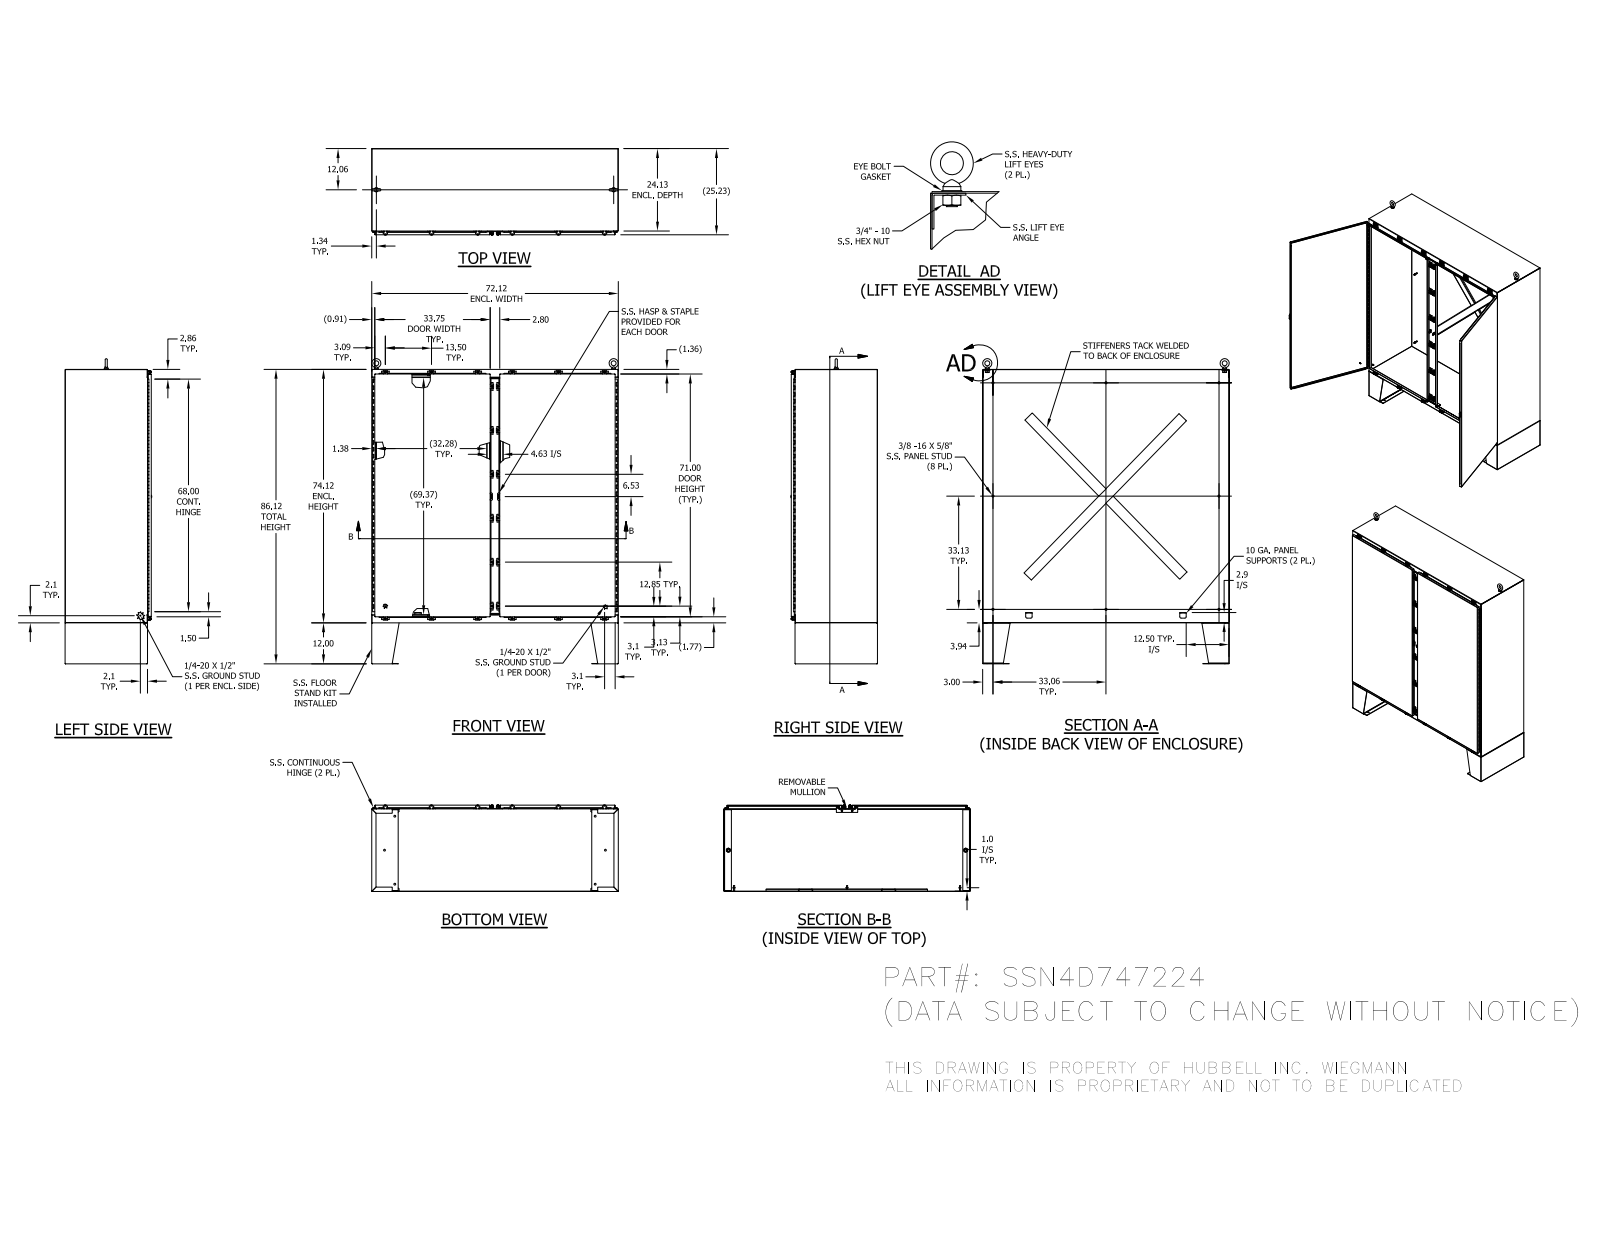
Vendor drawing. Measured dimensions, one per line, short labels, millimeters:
name: 328131P-68_1; SSFK24B_1; 32912_1; 30824_1 (+8 more)
written by: SolidWorks 2014 (AUTOMOTIVE_DESIGN)
unit: mm
bodies: 185 solids, 6996 faces (2802 planar, 2798 cylindrical, 1396 other)
size: 2266.9 × 1832 × 644
volume: 33 920 000 mm³; area: 28 090 000 mm²
holes: 48× ⌀2.8, 24× ⌀5.4, 24× ⌀7.1, 24× ⌀7.6, 18× ⌀14.3, 16× ⌀9.5, 4× ⌀5, 4× ⌀5.1, 4× ⌀7.9, 4× ⌀8, 2× ⌀3.6, 2× ⌀4
bosses: 31× ⌀6.4, 24× ⌀13.2, 24× ⌀12.7, 24× ⌀8.9, 10× ⌀8.4, 8× ⌀15.9, 4× ⌀11.1, 3× ⌀8.6
rounds: 268× R0.8, 62× R3.2, 48× R3.6, 39× R6.4, 34× R1.6, 24× R0.8, 24× R2.5, 16× R0.4
face distances: 2.4, 638.4, 636, 640.8, 1829.6, 1880.4, 1832, 610.4, 28, 1827.2
hole spacings: 342.9, 1825.3, 1848.9, 1853.4, 1861, 22.3, 22.3, 41.3
